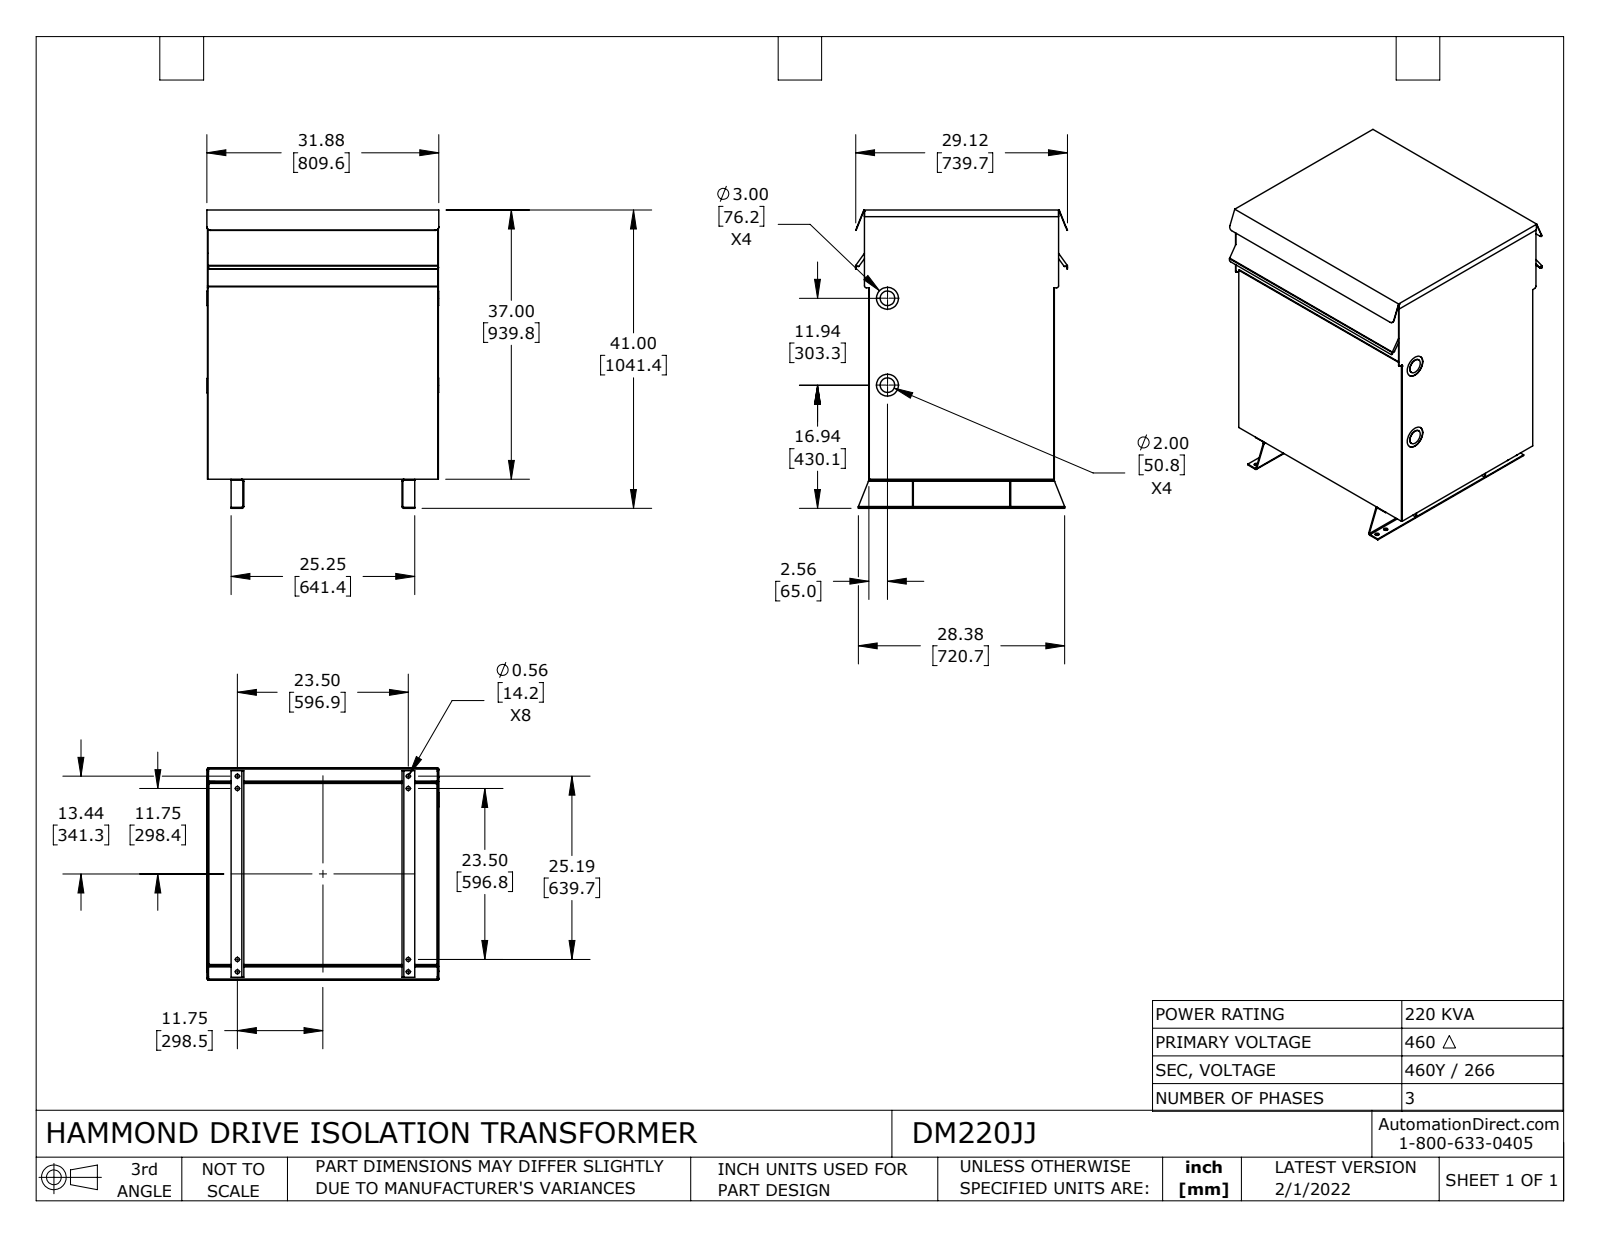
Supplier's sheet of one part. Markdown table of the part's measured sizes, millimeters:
| quantity | value |
| --- | --- |
| part name | DM220JJ |
| STEP written by | SolidWorks 2021 (CONFIG_CONTROL_DESIGN) |
| units | millimeters |
| bodies | 10 solids, 302 faces (192 planar, 106 cylindrical, 4 other) |
| overall size | 1041.4 × 809.6 × 740.2 |
| volume | 8 039 000 mm³ |
| surface area | 9 505 000 mm² |
| round holes (diameter × count) | 14.2 × 8, 76.2 × 4 |
| round bosses / shafts (diameter × count) | 50.8 × 4 |
| partial cylindrical surfaces (radius × count) | 1.5 × 4, 1.8 × 4, 2.7 × 4, 3 × 4, 3.2 × 4, 3.4 × 4, 3.6 × 4, 4.5 × 4 |
| main face-to-face distances | 1.5, 804.9, 646.2, 1.9, 806.5, 803.4, 644.7, 939.8, 938.3, 647.7 |
| hole center spacings | 42.9, 596.9, 598.4, 639.7, 874.9, 596.8, 682.6, 844 |
